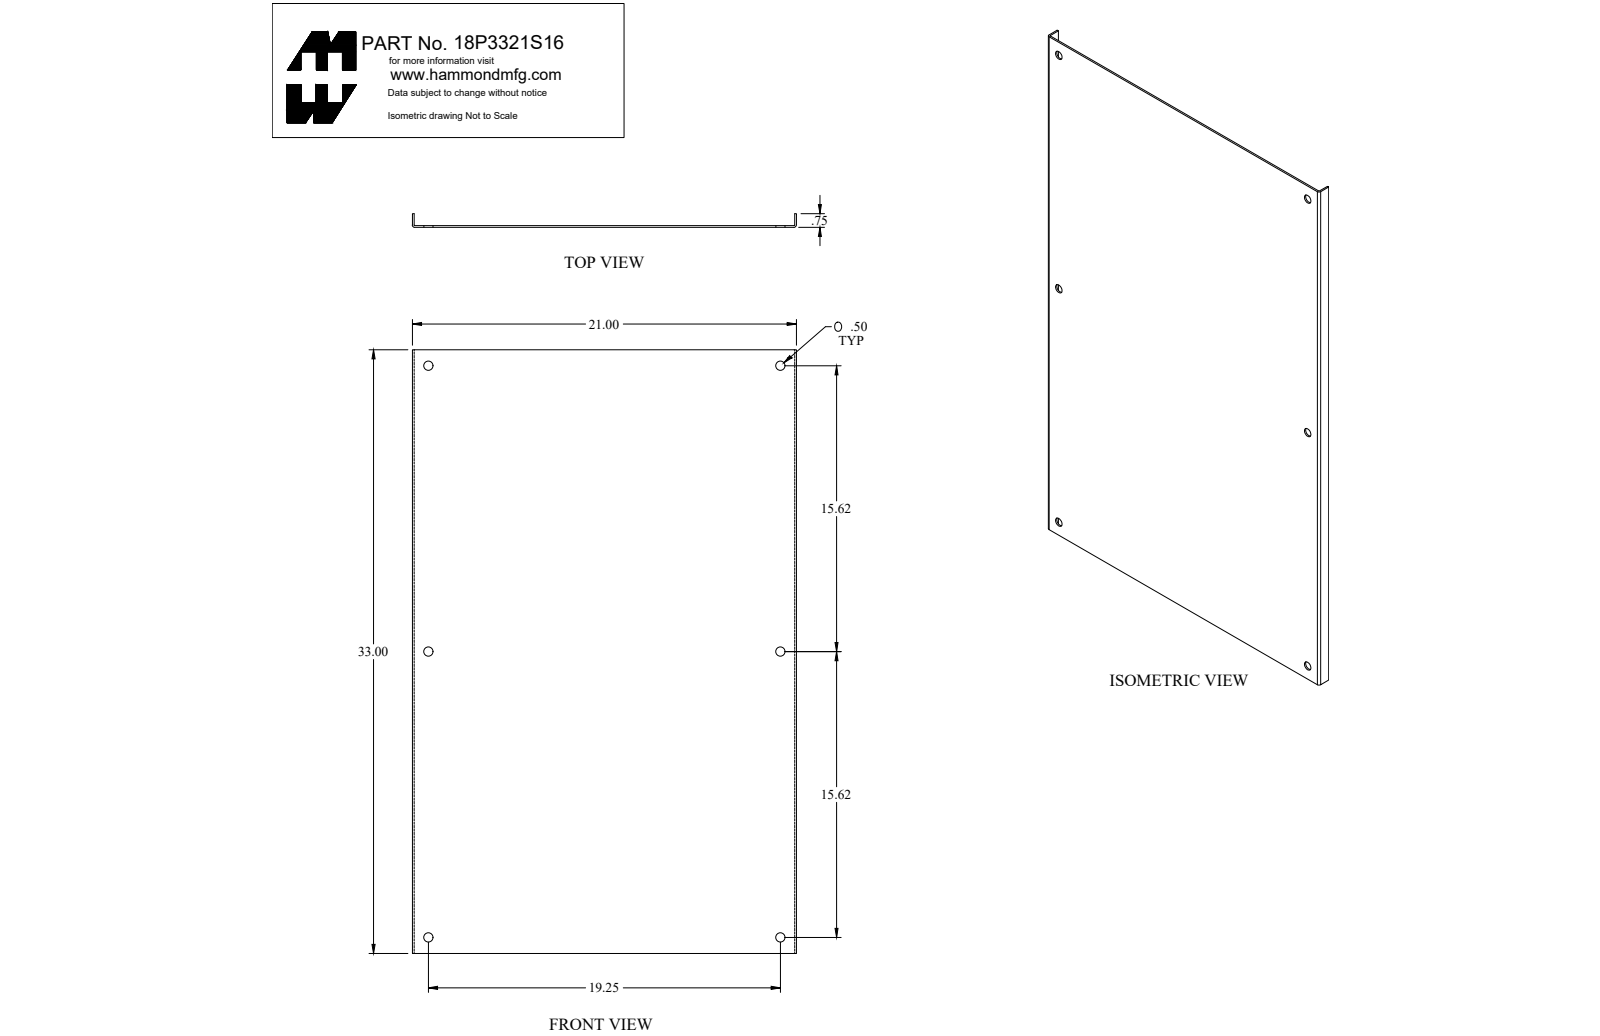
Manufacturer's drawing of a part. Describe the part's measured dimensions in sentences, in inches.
The part is named "18P3321S16_Default". Its 3-D file was written by "SolidWorks 2018 (CONFIG_CONTROL_DESIGN)". It is 1 solid with 26 faces: 10 planar, 16 cylindrical and 0 other. Overall it measures 33 by 21 by 0.75 inches. Its volume is 69.62 cubic inches and its surface area 1 477 square inches. Round holes: 6 of diameter 0.5. Partial cylindrical surfaces (rounded edges, fillets, slot ends): 2 of radius 0.03, 2 of radius 0.125. The main face-to-face distances are 0.095, 20.905, 21, 20.81, 0.75, 0.655, 33. The hole center spacings are 15.625, 24.793, 19.25, 31.25, 36.703.
